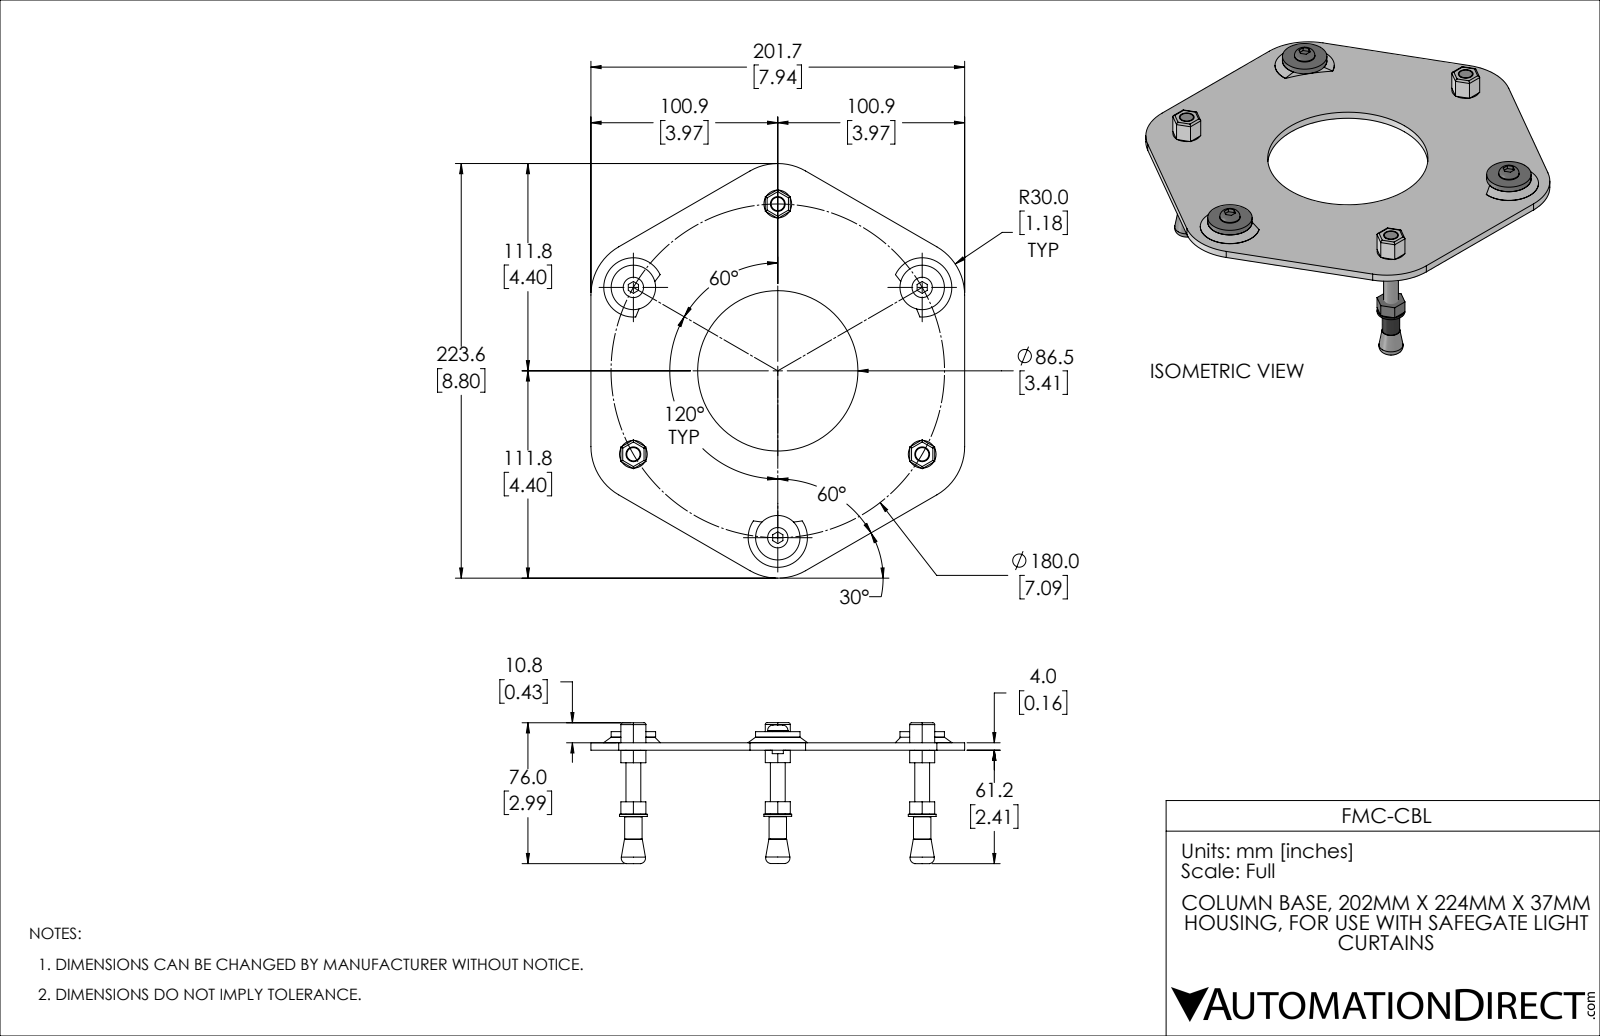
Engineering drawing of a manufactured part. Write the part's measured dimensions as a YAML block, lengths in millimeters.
part_name: "FMC-CBL"
step_written_by: "SolidWorks 2019 (AUTOMOTIVE_DESIGN)"
units: millimeters
bodies: {solids: 28, faces: 225, planar: 140, cylindrical: 70, other: 15}
overall_size: [223.6, 201.7, 76.1]
volume: 150300
surface_area: 85420
round_holes:
  - {diameter: 6, count: 3}
  - {diameter: 7.2, count: 3}
  - {diameter: 8, count: 3}
  - {diameter: 8.5, count: 3}
  - {diameter: 10, count: 3}
  - {diameter: 86.5, count: 1}
round_bosses_or_shafts:
  - {diameter: 24, count: 3}
  - {diameter: 15, count: 3}
  - {diameter: 11, count: 3}
  - {diameter: 9.4, count: 3}
partial_cylinders:
  - {radius: 1, count: 18}
  - {radius: 30, count: 6}
  - {radius: 16, count: 3}
  - {radius: 82, count: 1}
face_to_face_distances: [4, 3, 78, 7, 13.5, 155.9, 16.2, 185.5, 94.1, 107.6]
hole_center_spacings: [90, 155.9, 180]
